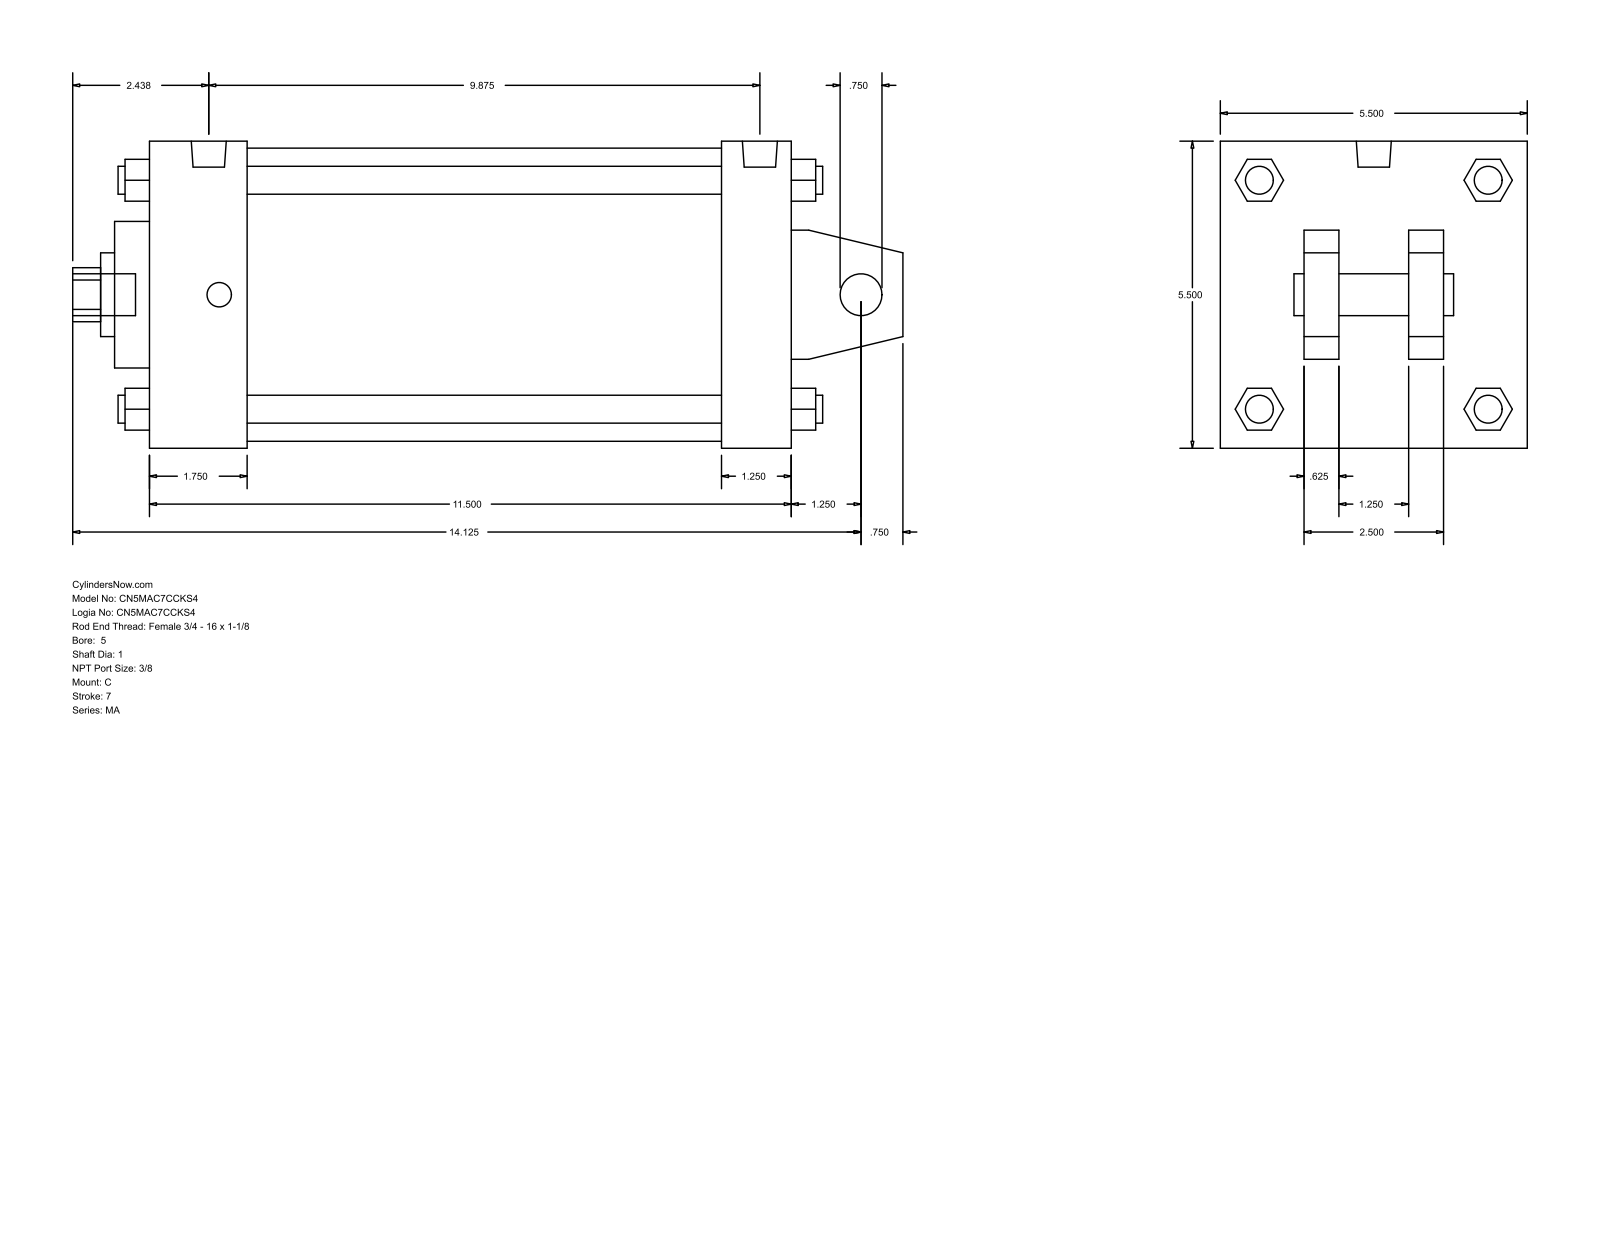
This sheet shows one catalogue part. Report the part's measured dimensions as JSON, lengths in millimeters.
{"part_name": "MA_C__0500_1", "step_written_by": "GSSL Pune (CONFIG_CONTROL_DESIGN)", "units": "millimeters", "bodies": {"solids": 0, "faces": 141, "planar": 109, "cylindrical": 32, "other": 0}, "overall_size": [377.82, 139.7, 139.7], "round_holes": [[19.05, 1], [25.4, 1], [38.1, 1], [66.67, 1], [133.35, 1]], "round_bosses_or_shafts": [[12.7, 4], [11.11, 4], [15.93, 2], [19.05, 1]], "partial_cylinders_radius": [[12.29, 1]], "face_to_face_distances": [139.7, 292.1, 15.87, 260.35, 31.75, 44.46, 215.89, 247.64, 38.1, 101.6]}
